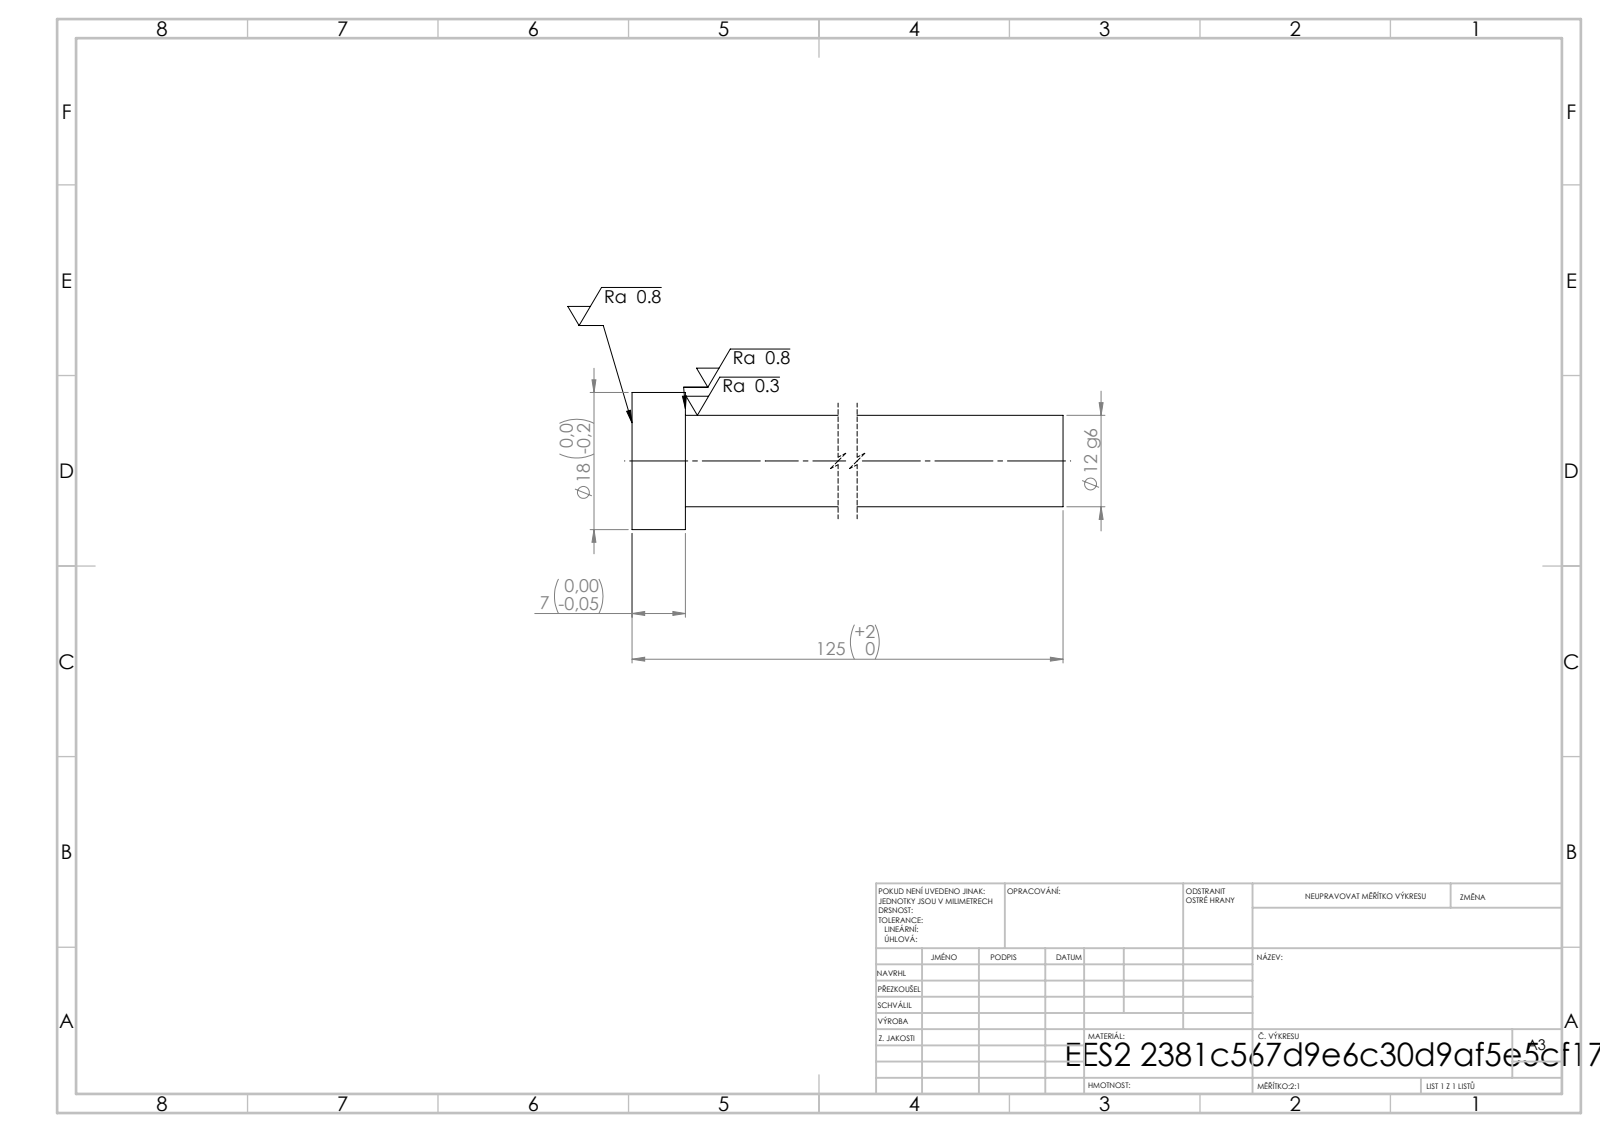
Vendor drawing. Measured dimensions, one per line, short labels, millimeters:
written by: SolidWorks 2019 (CONFIG_CONTROL_DESIGN)
unit: mm
bodies: 1 solid, 7 faces (3 planar, 4 cylindrical, 0 other)
size: 125 × 18 × 18
volume: 15 127 mm³; area: 5 353 mm²
bosses: 1× ⌀18, 1× ⌀12
face distances: 7, 125, 118
